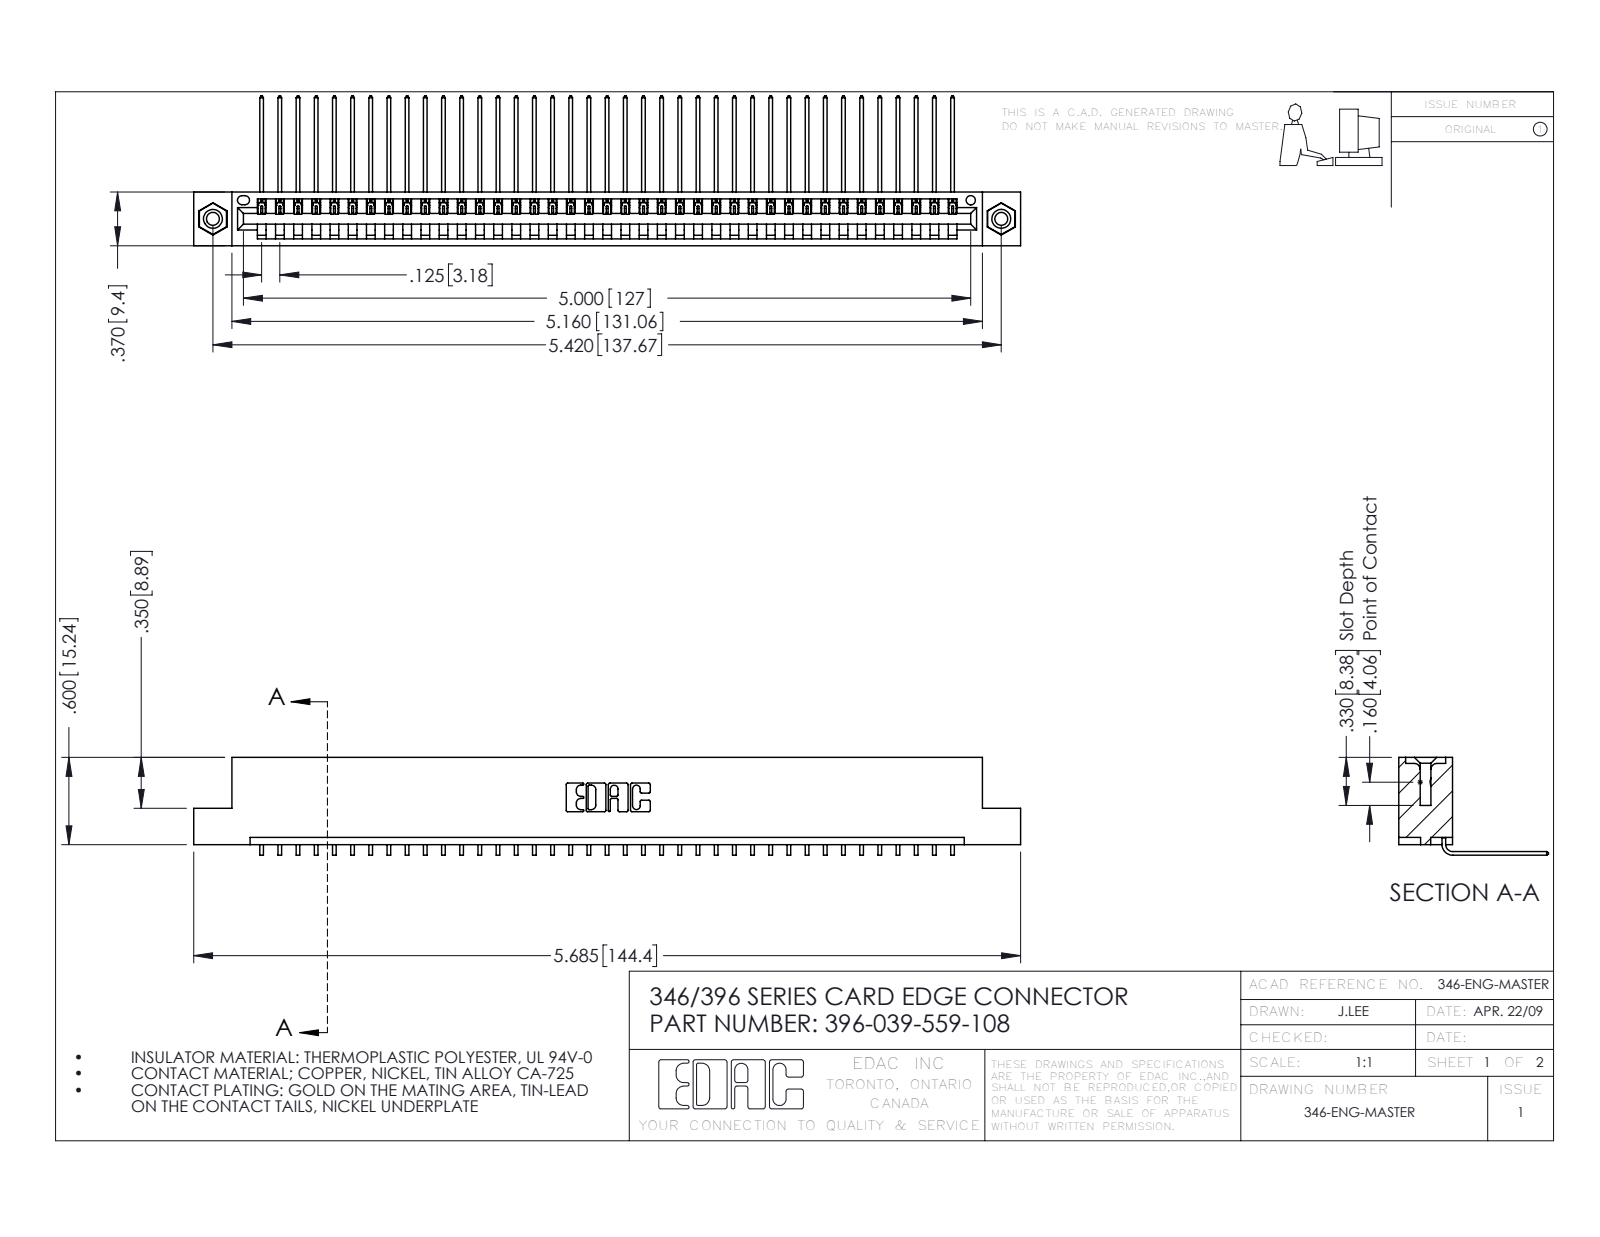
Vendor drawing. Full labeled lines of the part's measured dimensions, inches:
Part name (STEP PRODUCT): 345-292-001_558 559 Tail - 1; 396-039-559-108; 345-250-001_345-250-003-102; 346 Part_Flush Mounting Lugs - 0.156 Dia-TI
STEP written by: SolidWorks 2016 (CONFIG_CONTROL_DESIGN)
Units: inches
Bodies: 42 solids, 2522 faces (1746 planar, 760 cylindrical, 16 other)
Overall size (bounding box): 5.685 × 1.03 × 0.673
Volume: 0.85 in³ · Surface area: 28.16 in²
Round holes (diameter × count): ⌀0.089 ×2, ⌀0.125 ×2, ⌀0.156 ×2, ⌀0.064 ×1
Round bosses / shafts (diameter × count): ⌀0.155 ×2
Partial cylindrical surfaces — rounded edges, fillets, slot ends (radius × count): R0.006 ×78, R0.01 ×22, R0.007 ×6, R0.031 ×6, R0.026 ×3, R0.031 ×2, R0.04 ×2, R0.014 ×1
Main face-to-face distances: 0.048, 0.322, 0.37, 0.25, 0.025, 0.072, 0.298, 0.148, 0.222, 0.1
Hole centre spacings: 0.246, 5.211, 5.42
